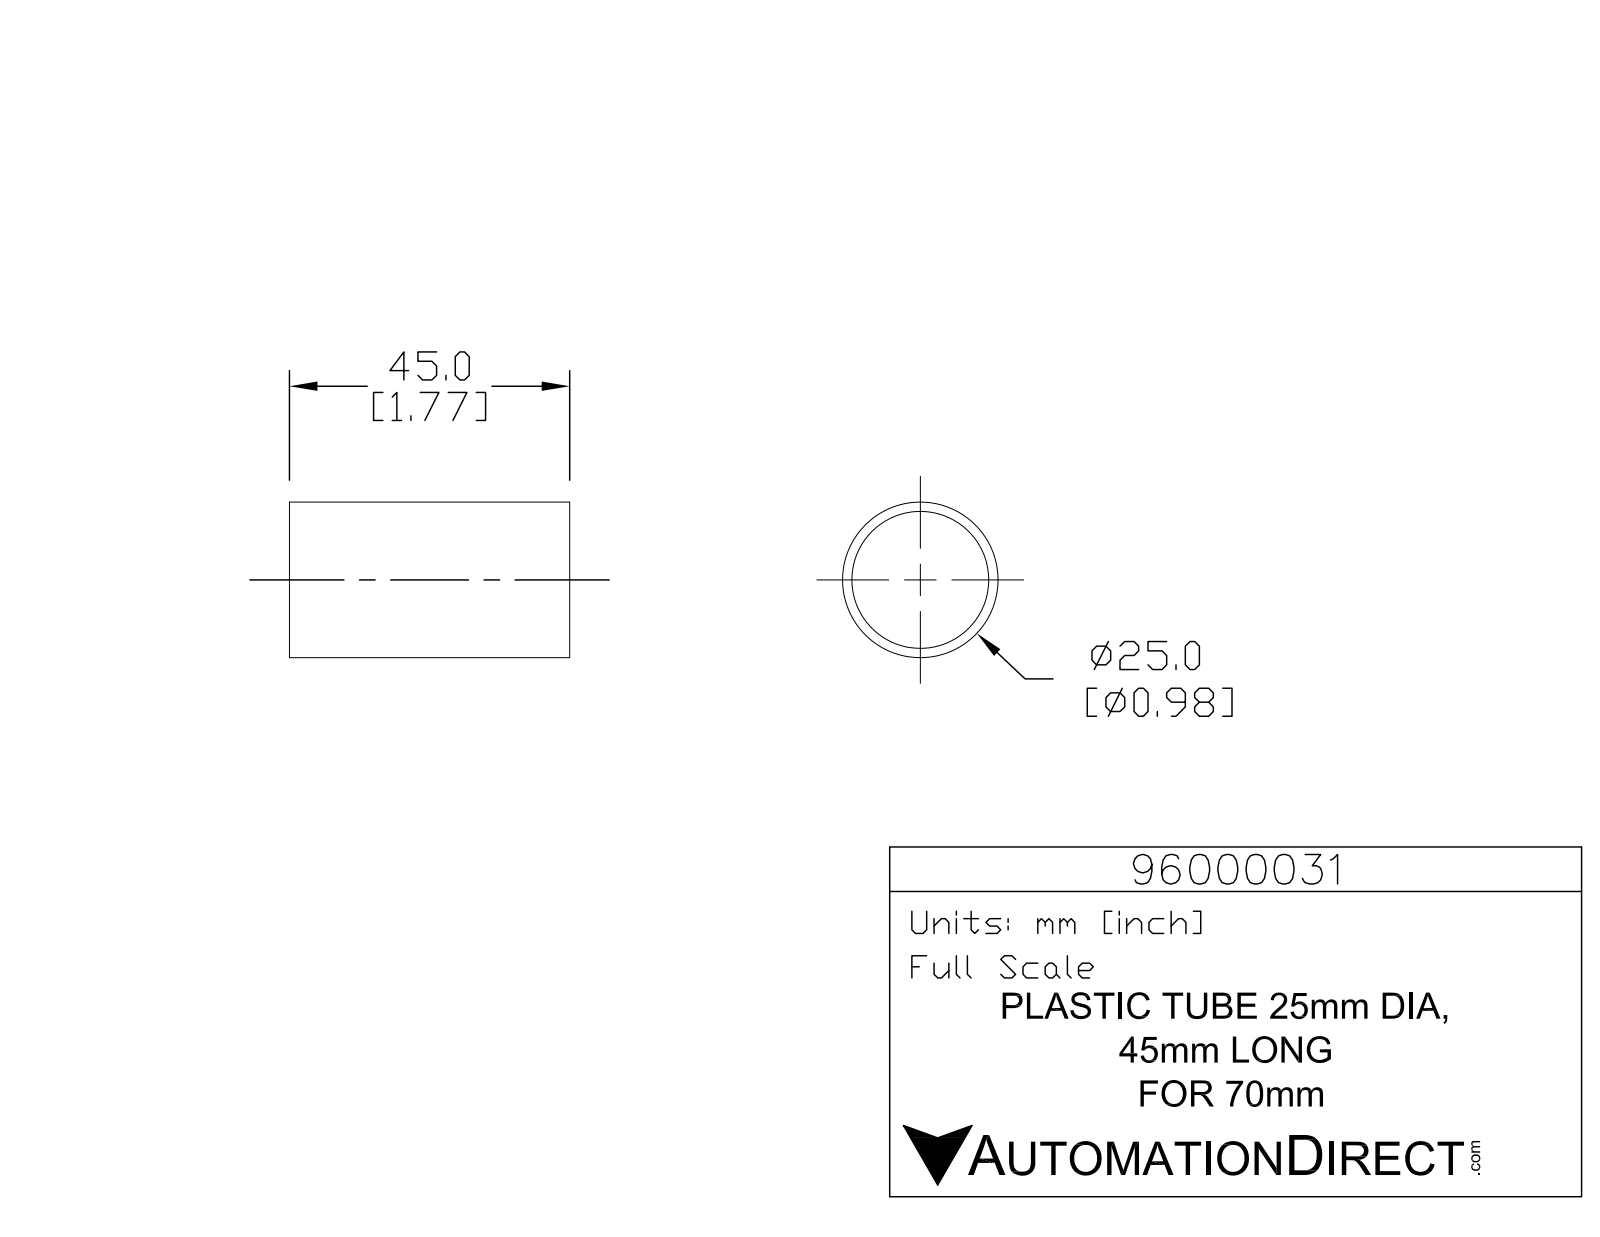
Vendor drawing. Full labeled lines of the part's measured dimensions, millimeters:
Part name (STEP PRODUCT): 96000031
STEP written by: SolidWorks 2015 (AUTOMOTIVE_DESIGN)
Units: millimetres
Bodies: 1 solid, 6 faces (2 planar, 4 cylindrical, 0 other)
Overall size (bounding box): 45 × 24.9 × 24.9
Volume: 4 640 mm³ · Surface area: 6 845 mm²
Round holes (diameter × count): ⌀22.1 ×1
Round bosses / shafts (diameter × count): ⌀24.9 ×1
Main face-to-face distances: 45
